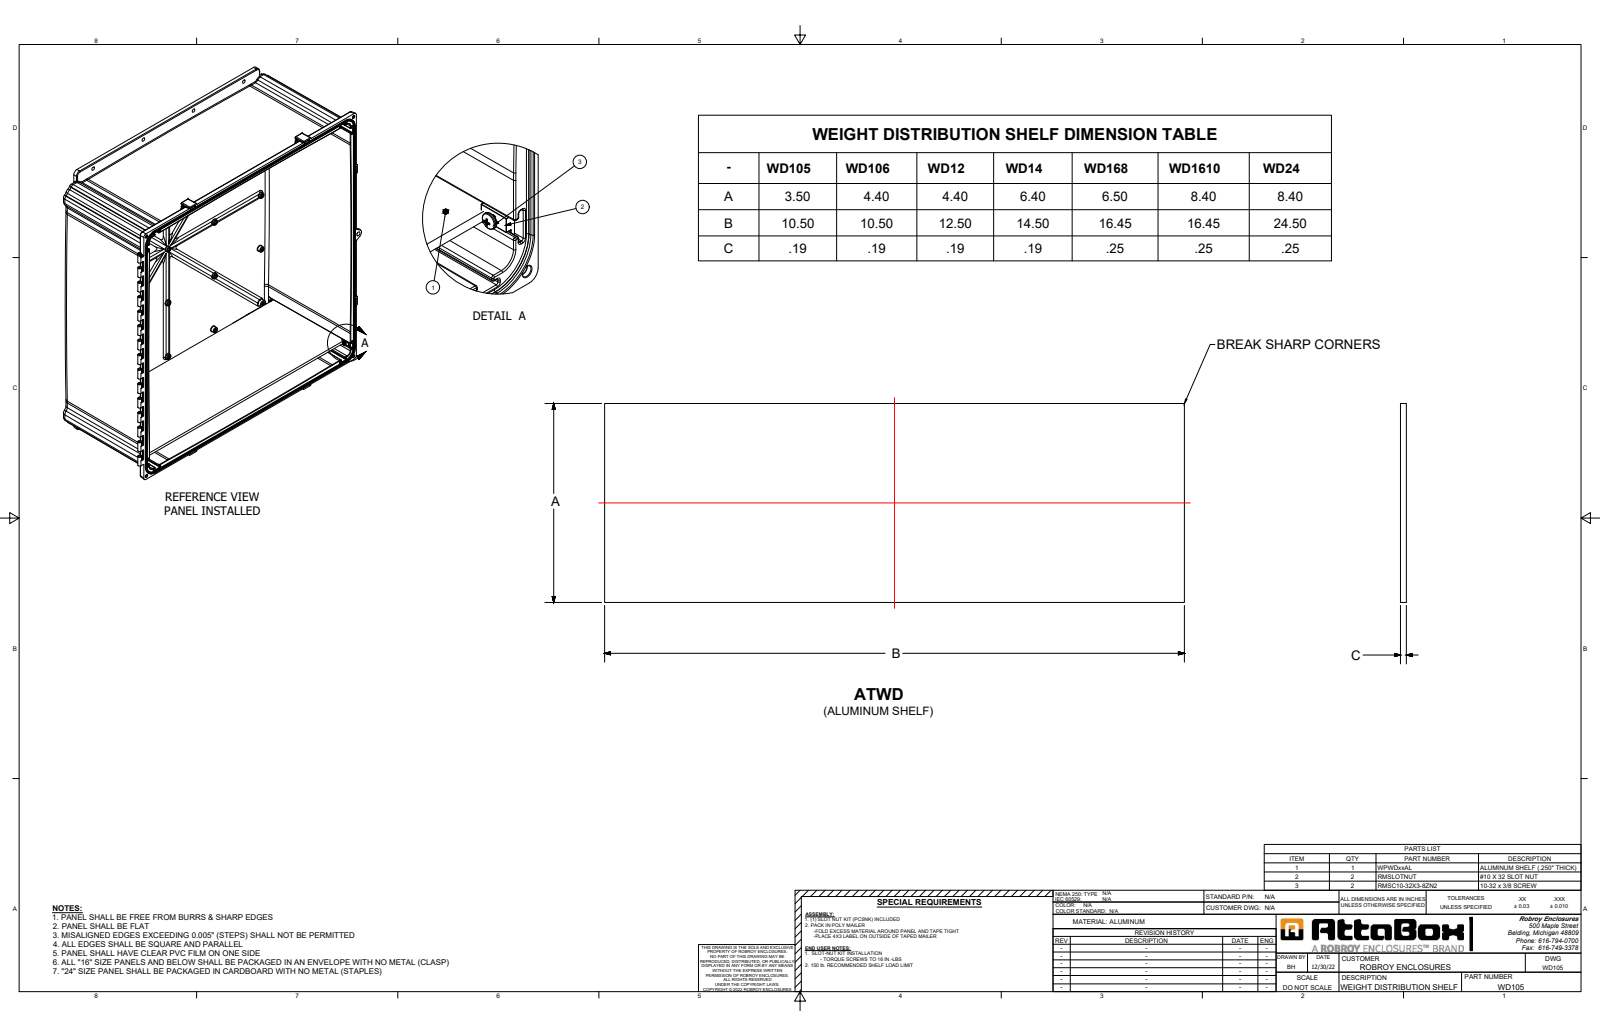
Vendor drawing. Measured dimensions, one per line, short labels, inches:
name: WD10-5_Default
written by: SolidWorks 2023 (CONFIG_CONTROL_DESIGN)
unit: in
bodies: 1 solid, 6 faces (6 planar, 0 cylindrical, 0 other)
size: 10.5 × 3.5 × 0.19
volume: 6.982 in³; area: 78.82 in²
face distances: 0.19, 3.5, 10.5
